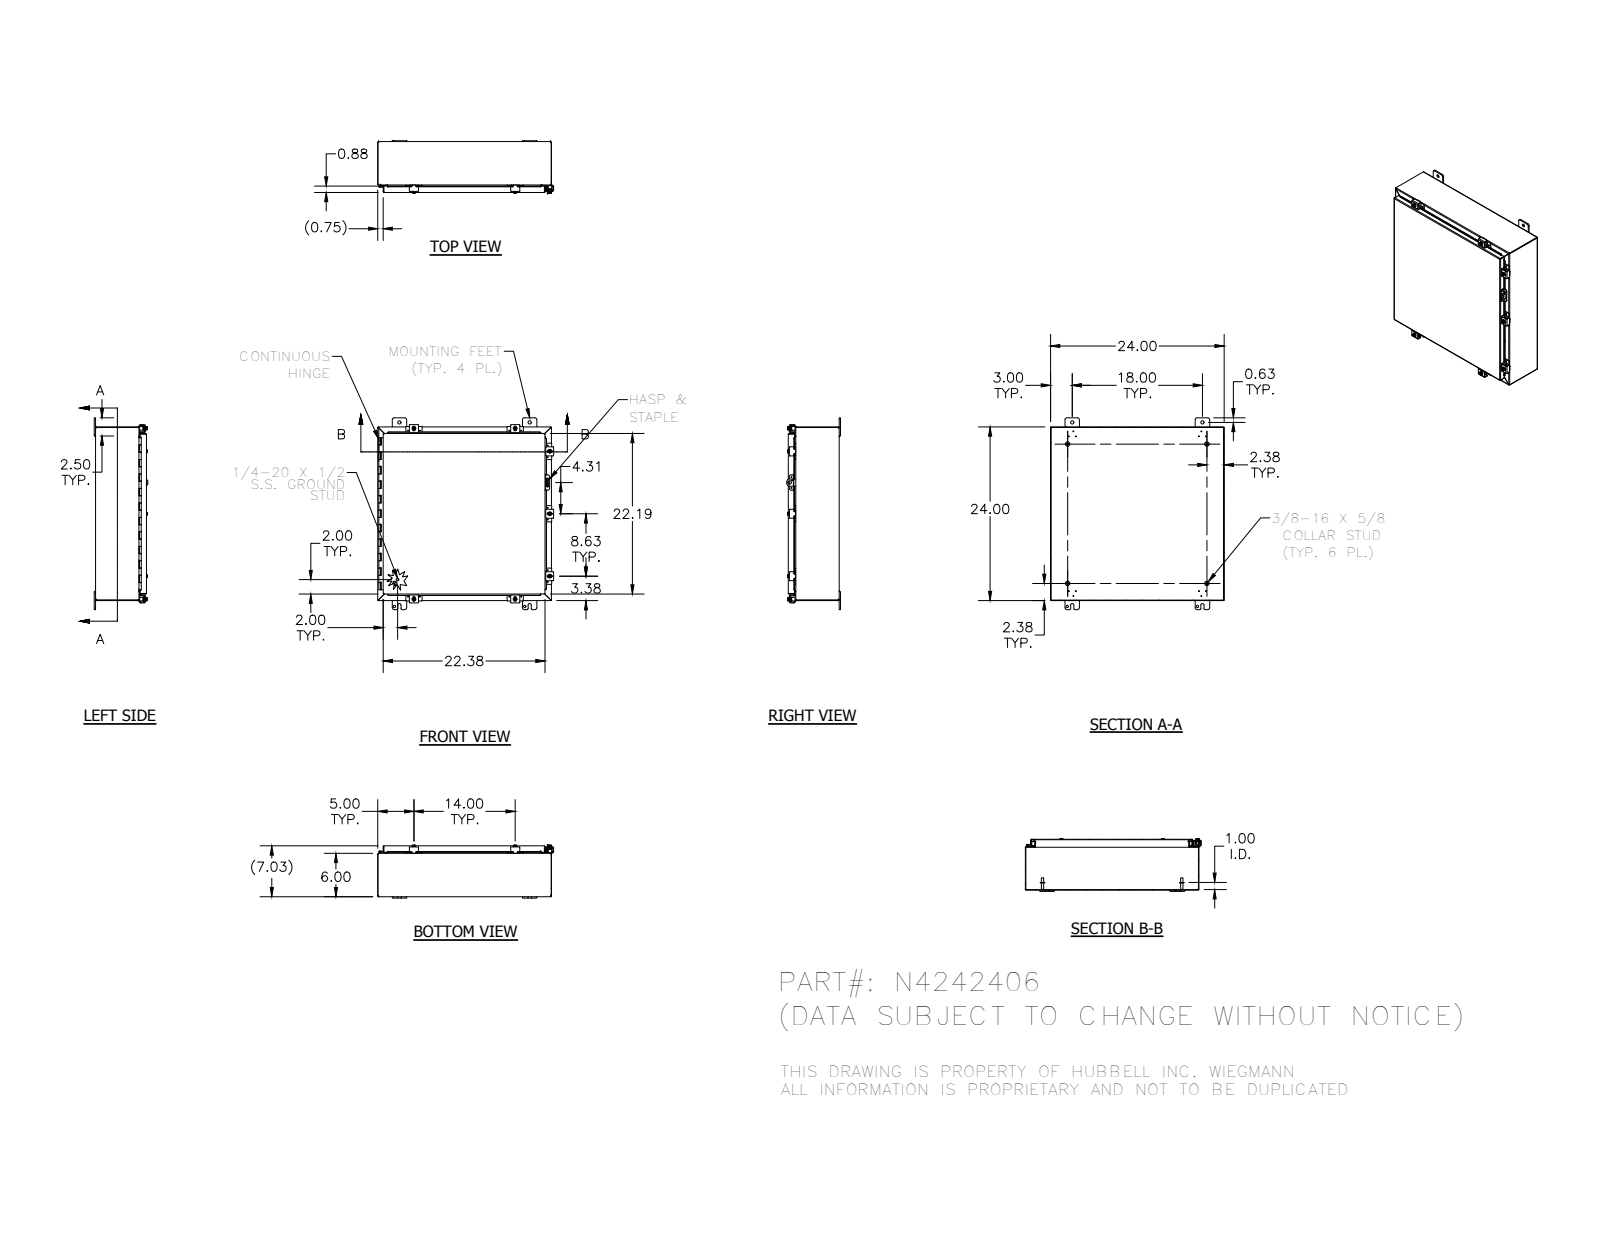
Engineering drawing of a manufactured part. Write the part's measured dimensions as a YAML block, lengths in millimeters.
part_name: "N4242406; 30824_1; N42424LID_1; HFW30825-3_1 (+8 more)"
step_written_by: "SolidWorks 2014 (AUTOMOTIVE_DESIGN)"
units: millimeters
bodies: {solids: 52, faces: 2242, planar: 856, cylindrical: 1003, other: 383}
overall_size: [673.1, 617.5, 188.2]
volume: 2660000
surface_area: 2725000
round_holes:
  - {diameter: 2.8, count: 17}
  - {diameter: 3, count: 12}
  - {diameter: 5.4, count: 7}
  - {diameter: 7.1, count: 7}
  - {diameter: 7.6, count: 7}
  - {diameter: 8, count: 4}
  - {diameter: 11.1, count: 4}
  - {diameter: 3.2, count: 1}
  - {diameter: 4, count: 1}
  - {diameter: 12.7, count: 1}
round_bosses_or_shafts:
  - {diameter: 6.4, count: 9}
  - {diameter: 13.2, count: 7}
  - {diameter: 12.7, count: 7}
  - {diameter: 8.9, count: 7}
  - {diameter: 15.9, count: 4}
  - {diameter: 8.4, count: 4}
  - {diameter: 2.9, count: 2}
  - {diameter: 8.6, count: 1}
partial_cylinders:
  - {radius: 0.8, count: 83}
  - {radius: 1.6, count: 47}
  - {radius: 3.2, count: 37}
  - {radius: 6.4, count: 33}
  - {radius: 0.8, count: 23}
  - {radius: 2.7, count: 23}
  - {radius: 3.6, count: 14}
  - {radius: 2.5, count: 10}
face_to_face_distances: [1.9, 176.8, 607.7, 174.9, 178.6, 605.8, 609.6, 150.5, 26.2, 152.4]
hole_center_spacings: [457.2, 22.3, 19.3, 21.3, 23.9, 24.6, 50.7, 441.2]
